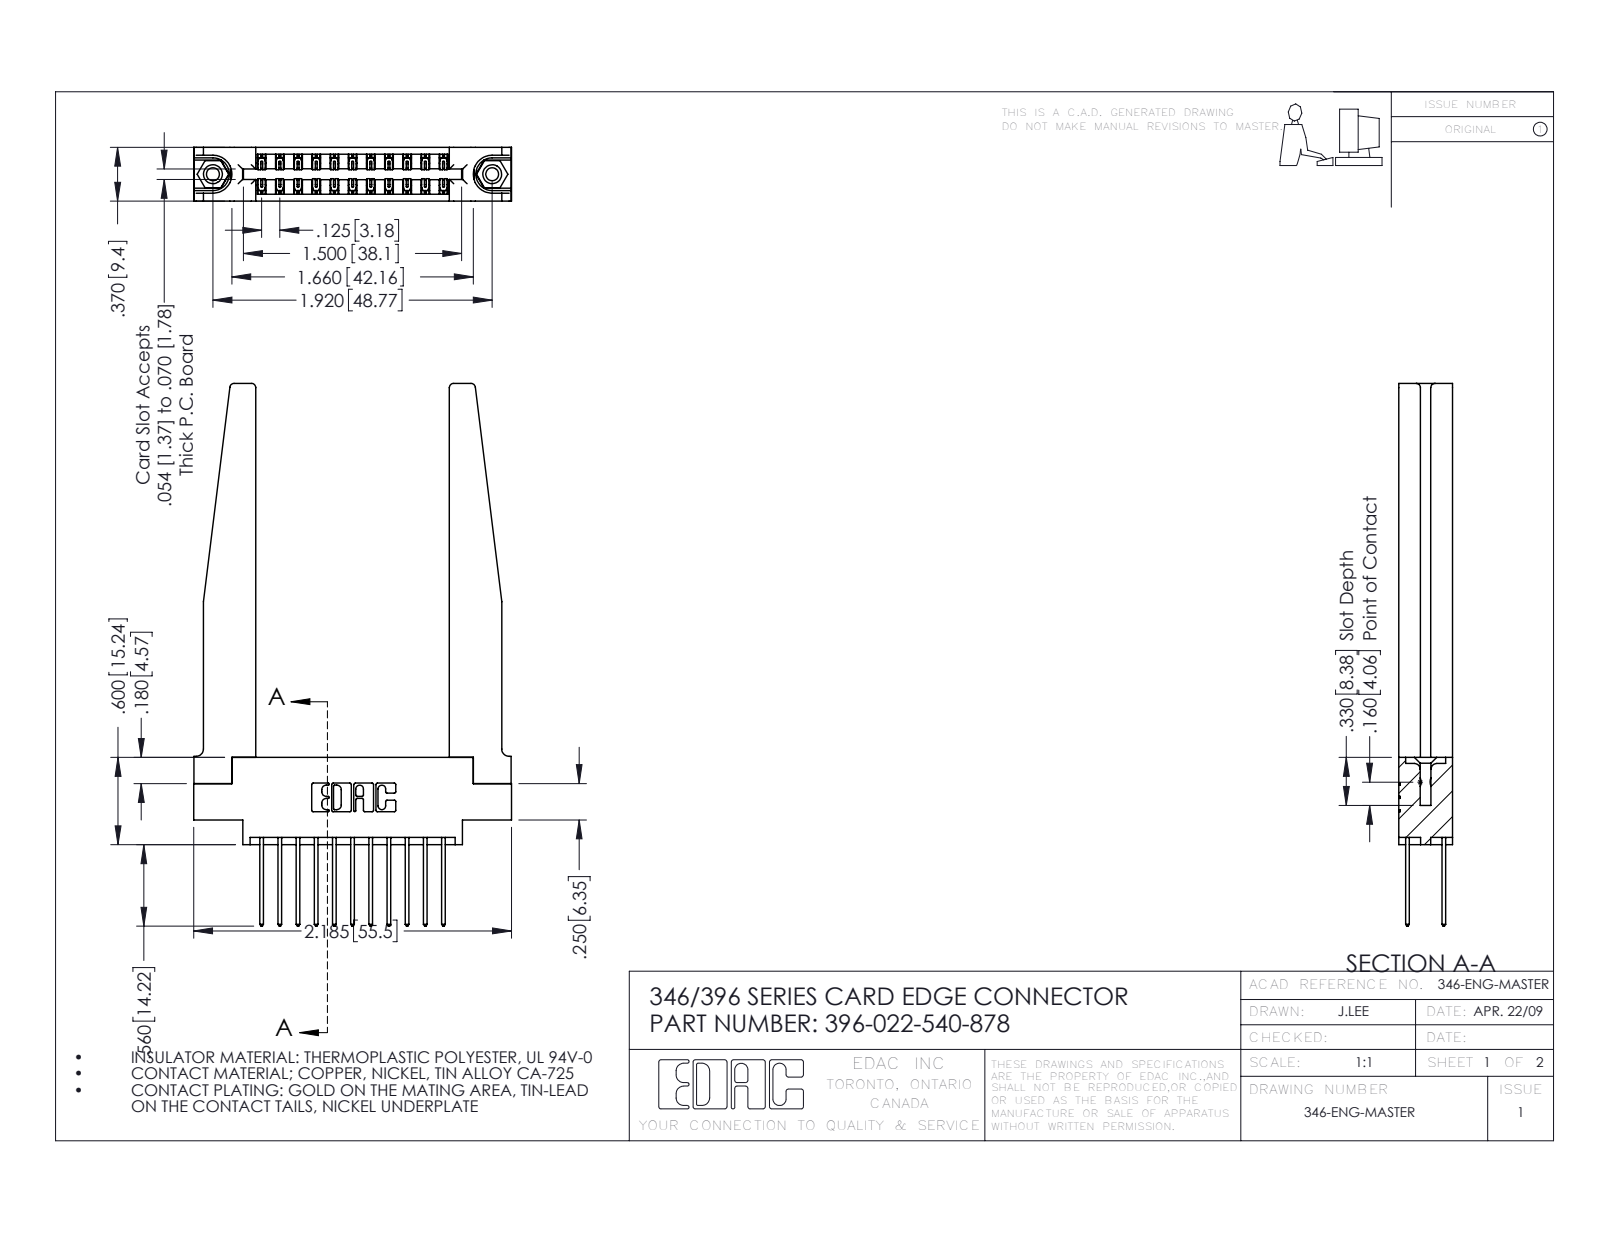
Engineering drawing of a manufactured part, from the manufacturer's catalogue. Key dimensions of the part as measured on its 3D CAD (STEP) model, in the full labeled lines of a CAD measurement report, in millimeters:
Part name (STEP PRODUCT): 345-292-001_345-293-140; 345-250-001_345-250-001-102; 346 Part_0.170 Offset - 0.156 Dia-TH; 396-022-540-878 (+1 more)
STEP written by: SolidWorks 2016 (CONFIG_CONTROL_DESIGN)
Units: millimetres
Bodies: 27 solids, 1504 faces (992 planar, 460 cylindrical, 52 other)
Overall size (bounding box): 94.7 × 55.5 × 9.4
Volume: 12 000 mm³ · Surface area: 13 630 mm²
Round holes (diameter × count): ⌀2.3 ×2, ⌀3.2 ×2, ⌀4 ×2, ⌀1.6 ×1
Round bosses / shafts (diameter × count): ⌀3.9 ×2
Partial cylindrical surfaces — rounded edges, fillets, slot ends (radius × count): R0.2 ×33, R0.3 ×22, R0.3 ×22, R0.8 ×8, R0.2 ×6, R0.8 ×6, R0.7 ×3, R0.4 ×2
Main face-to-face distances: 9.4, 3.8, 1.8, 3.8, 1.2, 8.2, 6.4, 2.6, 5.6, 4.4
Hole centre spacings: 6.2, 43.6, 48.8
